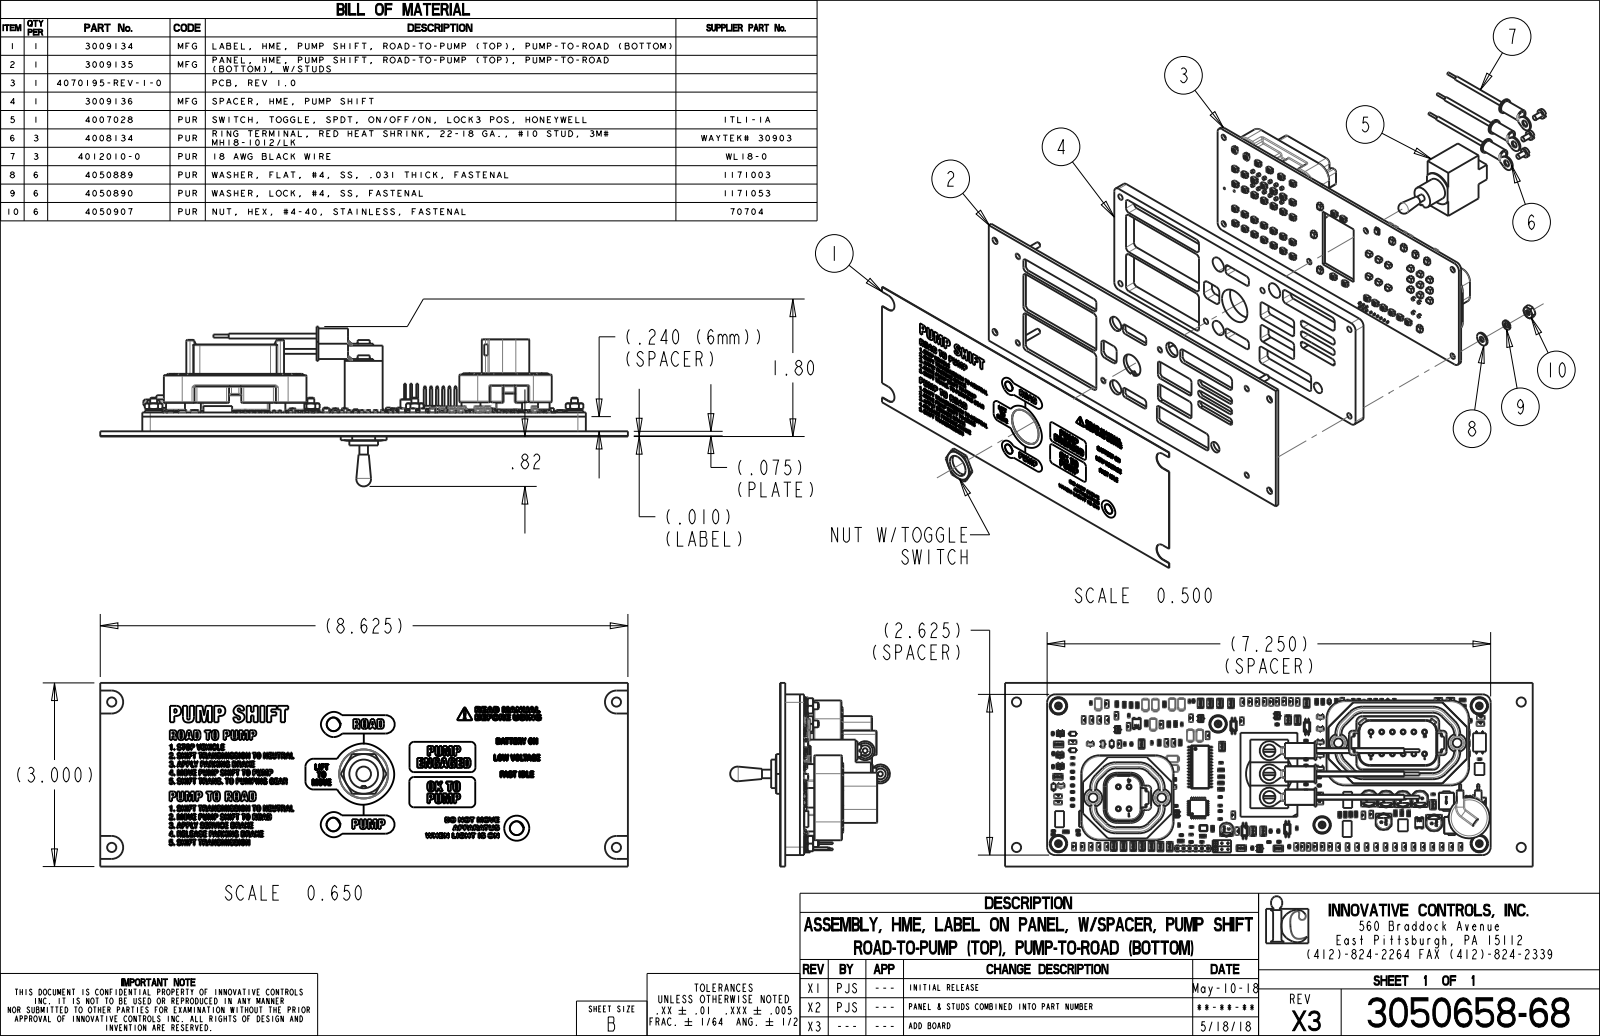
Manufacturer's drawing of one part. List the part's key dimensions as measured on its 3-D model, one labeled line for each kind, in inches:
Part name (STEP PRODUCT): 3009135; 4050902; 3009135_ASM; 3009134 (+8 more)
STEP written by: PRO/ENGINEER BY PARAMETRIC TECHNOLOGY CORPORATION, 2012360 (CONFIG_CONTROL_DESIGN)
Units: inches
Bodies: 630 solids, 39429 faces (16066 planar, 7482 cylindrical, 15881 other)
Overall size (bounding box): 8.625 × 3 × 2.611
Volume: 8.977 in³ · Surface area: 232.1 in²
Round holes (diameter × count): ⌀0.087 ×45, ⌀0.125 ×17, ⌀0.065 ×16, ⌀0.039 ×9, ⌀0.129 ×8, ⌀0.04 ×6, ⌀0.111 ×6, ⌀0.112 ×6, ⌀0.021 ×4, ⌀0.15 ×4, ⌀0.146 ×3, ⌀0.175 ×3
Round bosses / shafts (diameter × count): ⌀0.062 ×16, ⌀0.01 ×12, ⌀0.26 ×8, ⌀0.012 ×8, ⌀0.287 ×6, ⌀0.248 ×6, ⌀0.209 ×6, ⌀0.15 ×6
Partial cylindrical surfaces — rounded edges, fillets, slot ends (radius × count): R0.006 ×674, R0.005 ×328, R0.005 ×230, R0.008 ×216, R0.005 ×176, R0.004 ×122, R0.02 ×111, R0.01 ×108
Main face-to-face distances: 0.315, 0.075, 0.24, 0.085, 0.325, 0.067, 0.307, 0.393, 0.382, 2.625
Hole centre spacings: 0.35, 0.501, 0.175, 0.359, 0.399, 0.636, 0.687, 7.565
